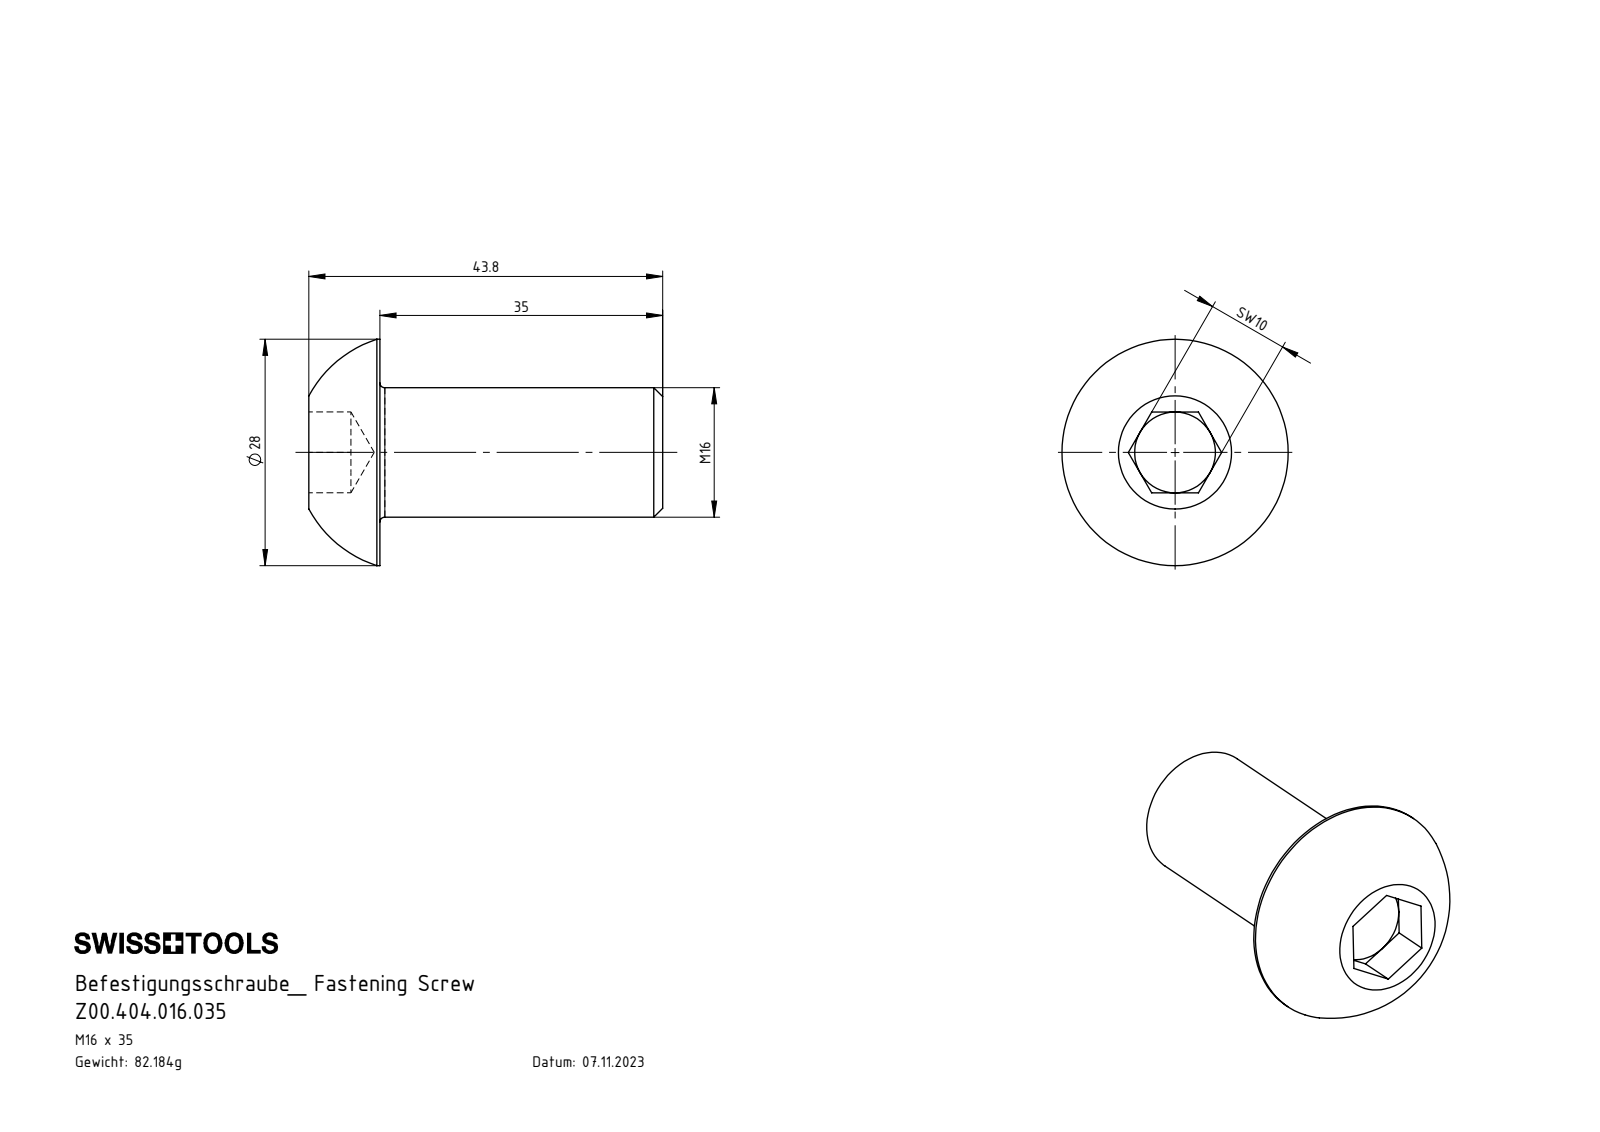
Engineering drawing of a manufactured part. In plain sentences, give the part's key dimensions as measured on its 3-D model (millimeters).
The part is named "Z00.404.016.035". Its 3-D file was written by "SolidWorks 2022 (AUTOMOTIVE_DESIGN)". It is 1 solid with 27 faces: 15 planar, 4 cylindrical and 8 other. Overall it measures 43.8 by 28 by 28 millimeters. Its volume is 10 273 cubic millimeters and its surface area 3 486 square millimeters. Round bosses or shafts: 1 of diameter 28, 1 of diameter 16. The main face-to-face distances are 35, 10, 8.8, 43.8, 5.2, 3.6, 38.6.
